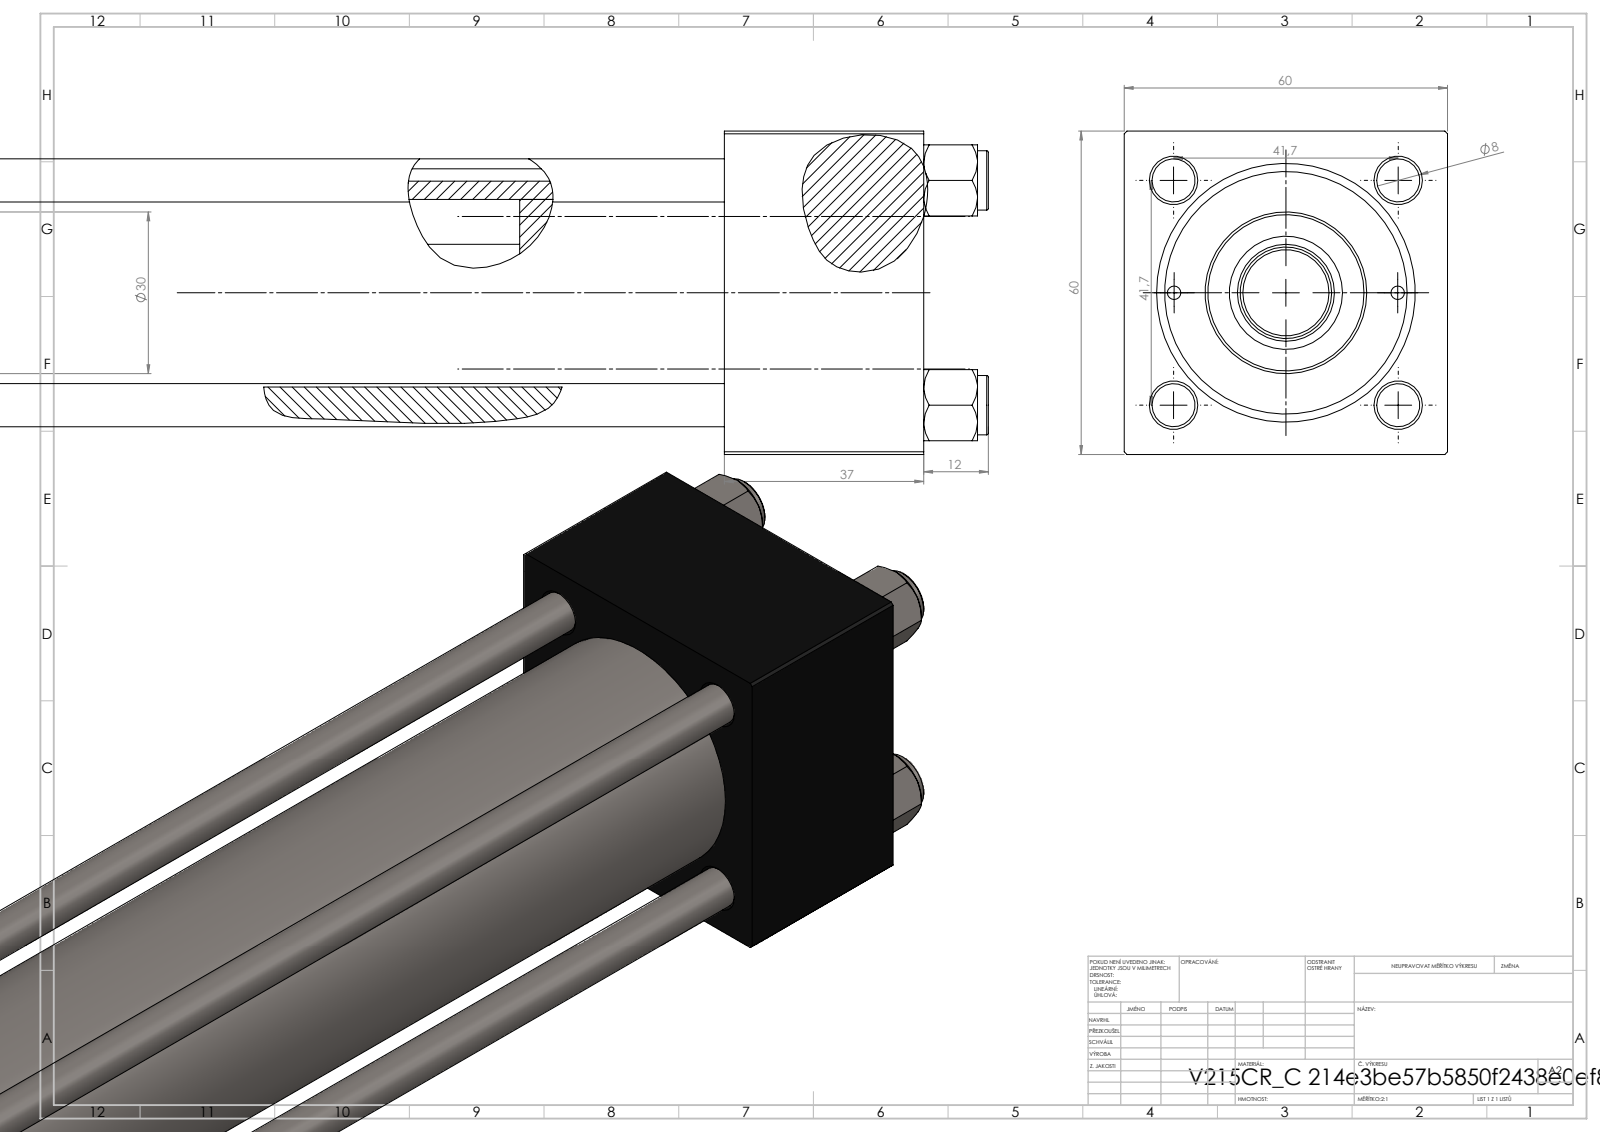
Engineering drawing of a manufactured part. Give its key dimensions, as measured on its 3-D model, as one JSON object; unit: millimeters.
{"part_name": "V215CR_VCP_C; NUT_M5_C; V215CR_ROD_END_F; V215CR_C_TYCINKA (+2 more)", "step_written_by": "SolidWorks 2019 (CONFIG_CONTROL_DESIGN)", "units": "millimeters", "bodies": {"solids": 12, "faces": 1165, "planar": 531, "cylindrical": 94, "other": 540}, "overall_size": [485, 60, 60], "volume_mm3": 646758, "surface_area_mm2": 226350, "round_holes": [[8, 4], [2.5, 2], [7, 2], [16.66, 2], [24, 2], [8.5, 1], [18, 1], [21, 1], [31, 1], [40, 1], [45, 1]], "round_bosses_or_shafts": [[11, 5], [46, 1], [30, 1], [17, 1]], "face_to_face_distances": [60, 37, 428, 391, 53, 375, 338, 399.3, 362.3, 24.3], "hole_center_spacings": [20.85, 29.49, 41.7, 46.53, 20.75, 58.97, 41.5, 372.5]}
